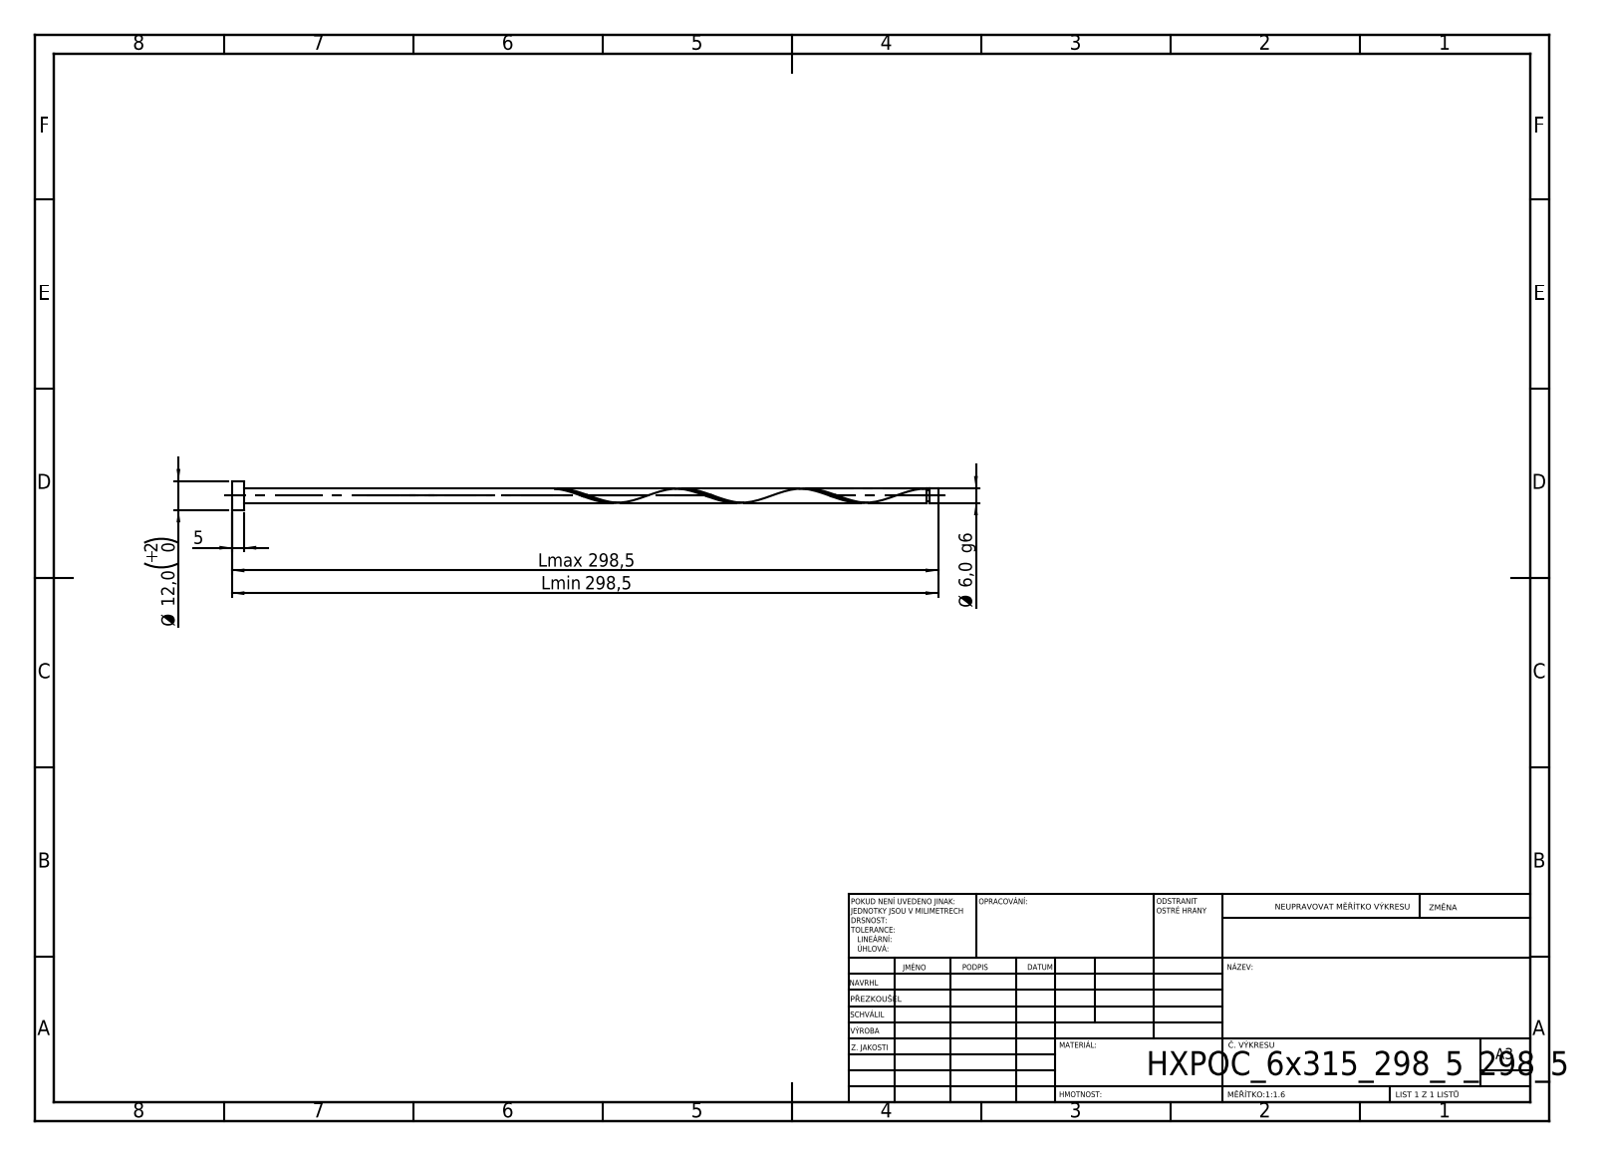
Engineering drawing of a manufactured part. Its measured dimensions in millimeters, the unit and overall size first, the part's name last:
Units: millimetres
Overall size (bounding box): 298.5 × 12 × 12
Round bosses / shafts (diameter × count): ⌀12 ×1, ⌀6 ×1, ⌀4.8 ×1
Main face-to-face distances: 5, 298.5, 293.5, 294.91, 289.91, 3.59, 293.71, 288.71, 1.2, 4.79
Volume: 8 767 mm³ · Surface area: 6 060 mm²
Bodies: 1 solid, 21 faces (6 planar, 14 cylindrical, 1 other)
STEP written by: SolidWorks 2019 (CONFIG_CONTROL_DESIGN)
